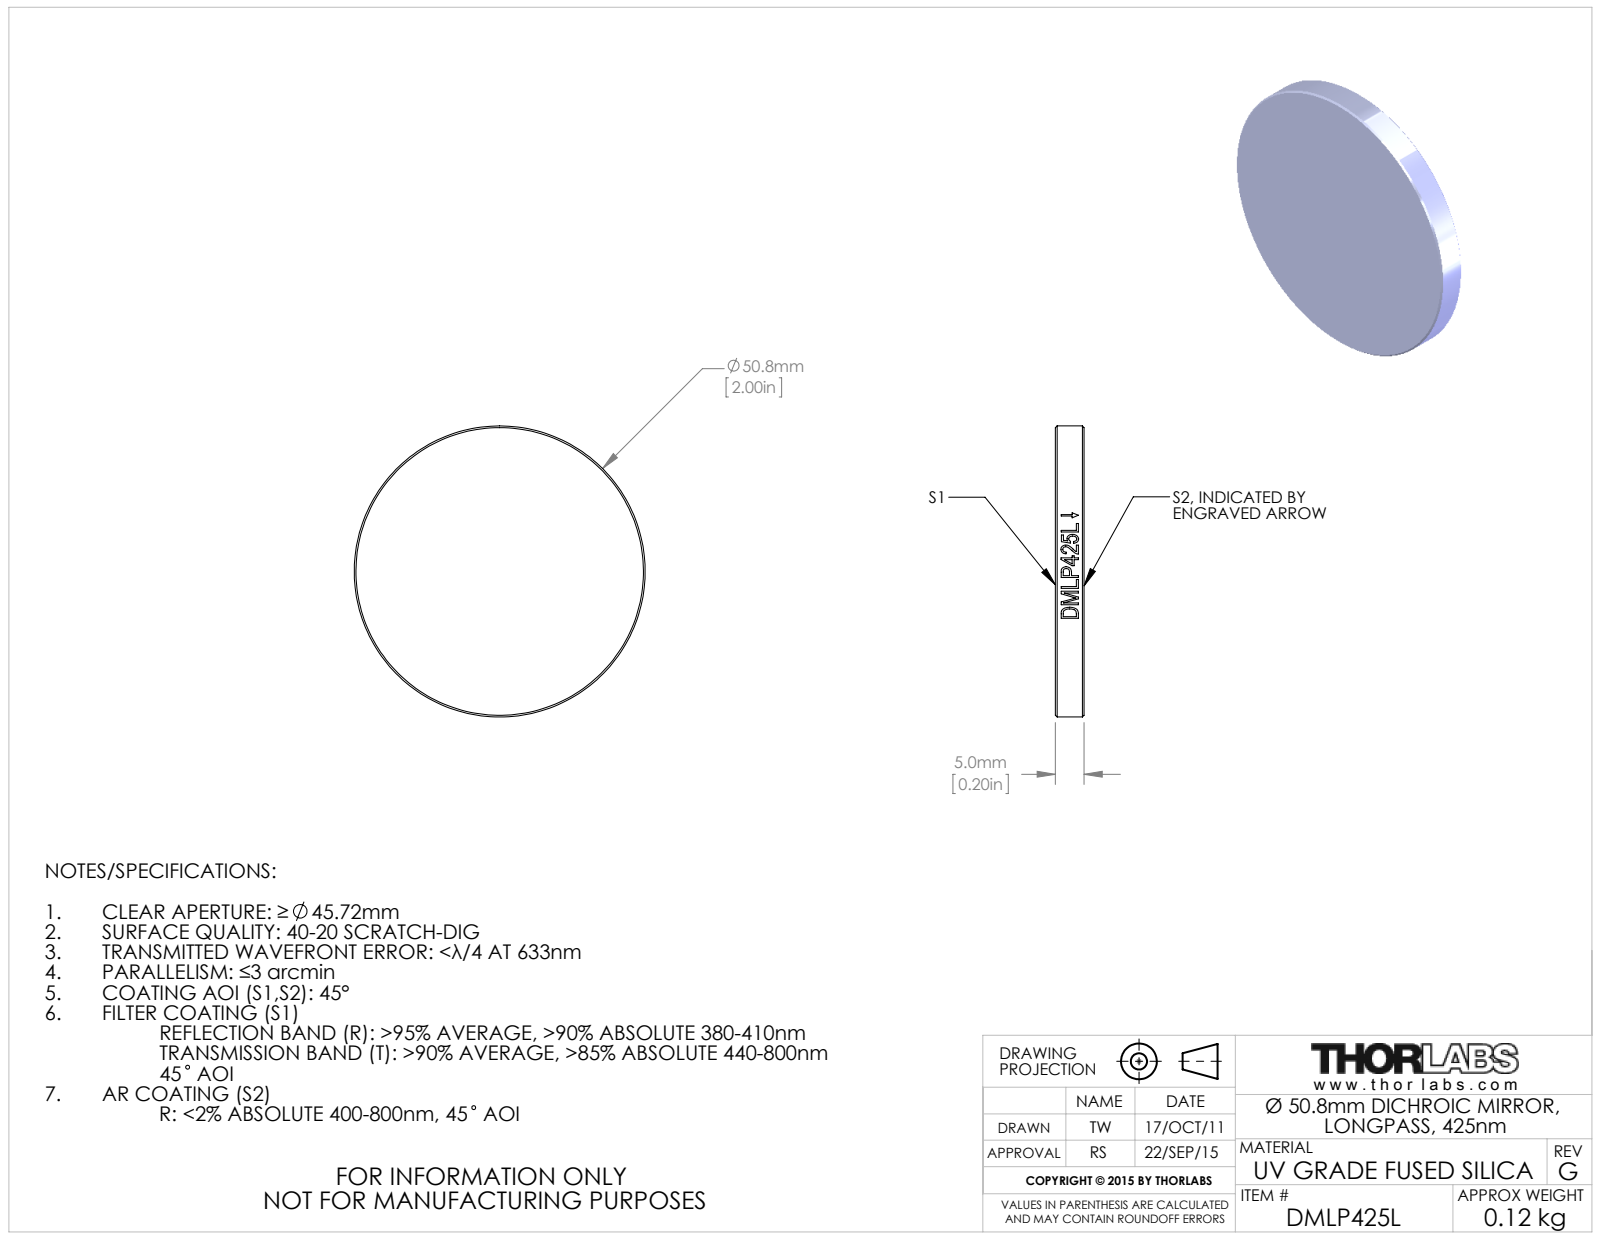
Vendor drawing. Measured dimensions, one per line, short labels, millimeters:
name: 21026-E0W
written by: SolidWorks 2011 (CONFIG_CONTROL_DESIGN)
unit: mm
bodies: 0 solids, 20 faces (2 planar, 14 cylindrical, 4 other)
size: 50.8 × 50.8 × 5
bosses: 1× ⌀50.8
face distances: 5
